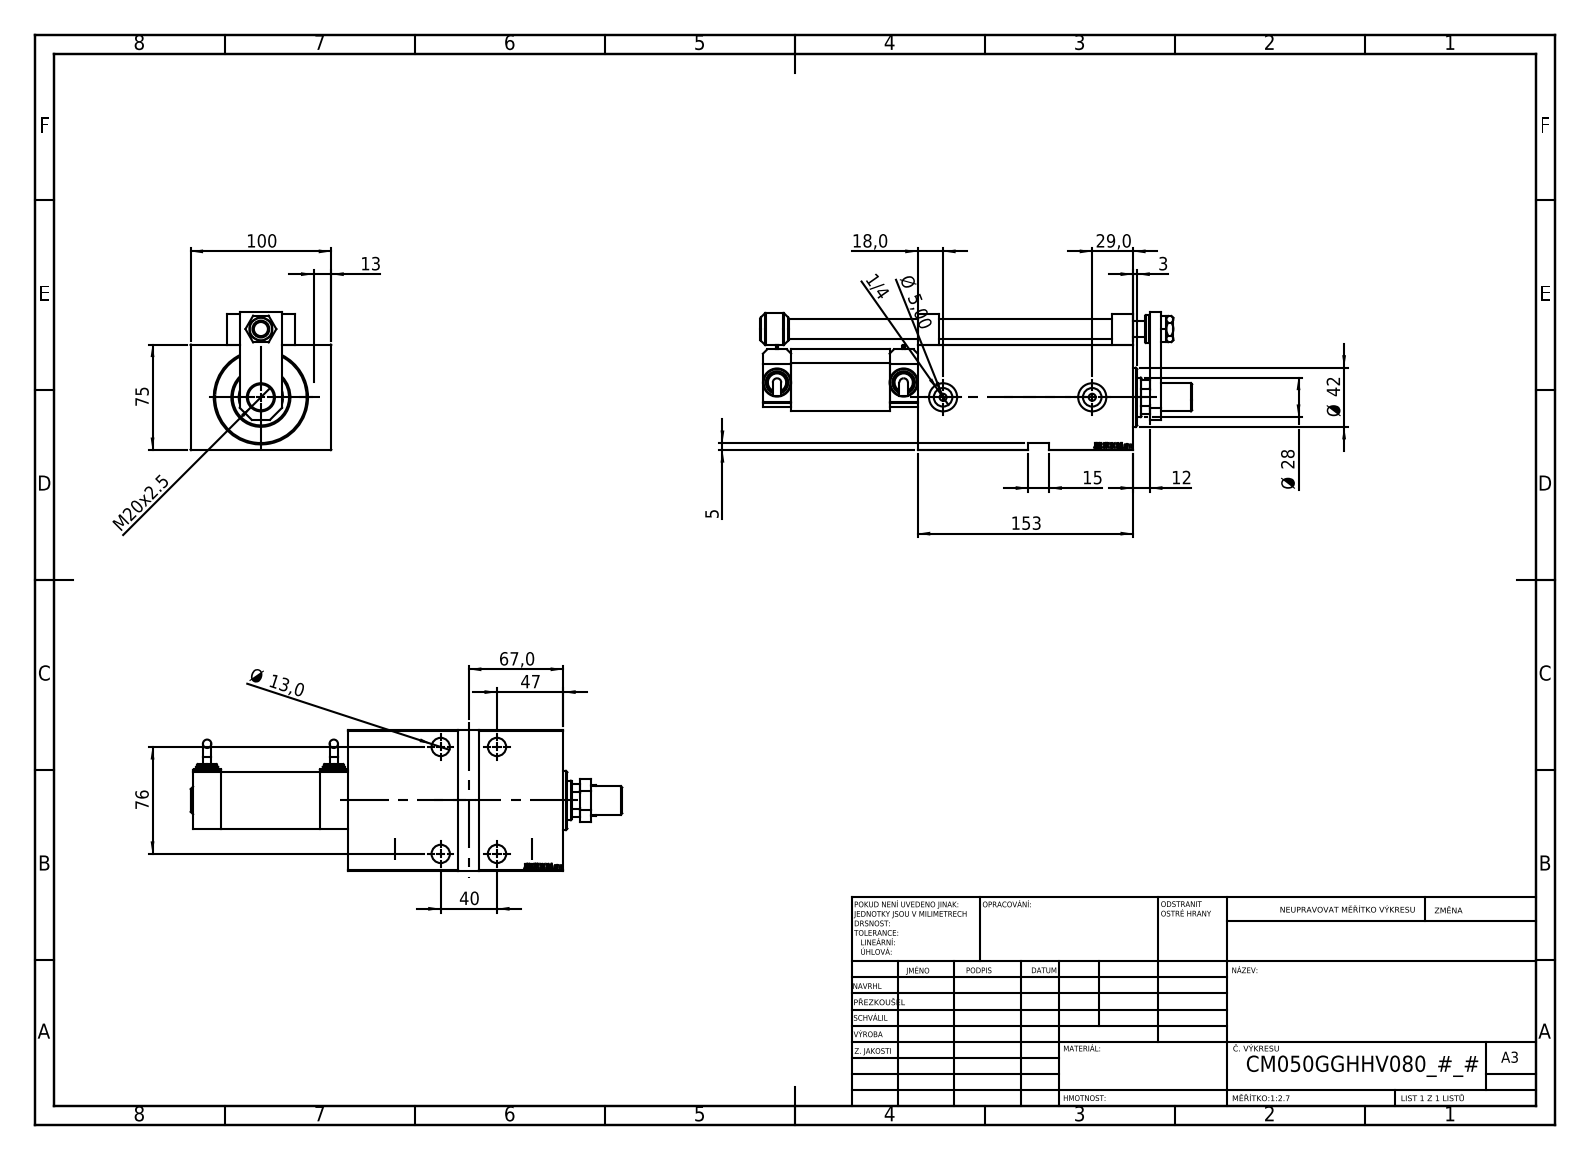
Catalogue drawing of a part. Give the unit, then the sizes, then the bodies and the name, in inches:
Units: inches
Overall size (bounding box): 12.079 × 3.937 × 3.858
Round holes (diameter × count): ⌀0.512 ×5, ⌀0.157 ×4, ⌀0.315 ×4, ⌀0.748 ×4, ⌀0.787 ×3, ⌀0.197 ×2, ⌀0.518 ×2, ⌀0.472 ×1, ⌀0.551 ×1, ⌀0.728 ×1, ⌀1.102 ×1, ⌀1.24 ×1
Round bosses / shafts (diameter × count): ⌀0.787 ×3, ⌀0.709 ×3, ⌀0.63 ×2, ⌀0.551 ×2, ⌀0.236 ×2, ⌀1.654 ×1, ⌀0.906 ×1
Partial cylindrical surfaces — rounded edges, fillets, slot ends (radius × count): R0.118 ×1, R0.531 ×1
Main face-to-face distances: 2.953, 2.756, 3.937, 1.181, 0.197, 6.024, 0.787, 6.811, 3.543, 4.094
Hole centre spacings: 0.787, 1.575, 1.906, 2.447, 2.554, 2.979, 2.992, 3.319
Volume: 76.22 in³ · Surface area: 312 in²
Bodies: 17 solids, 1133 faces (556 planar, 118 cylindrical, 459 other)
Part name (STEP PRODUCT): V450CM_VC_G; V450CM_G_Body; MIDDLE; V450CM_G_VCP (+7 more)
STEP written by: SolidWorks 2019 (CONFIG_CONTROL_DESIGN)
